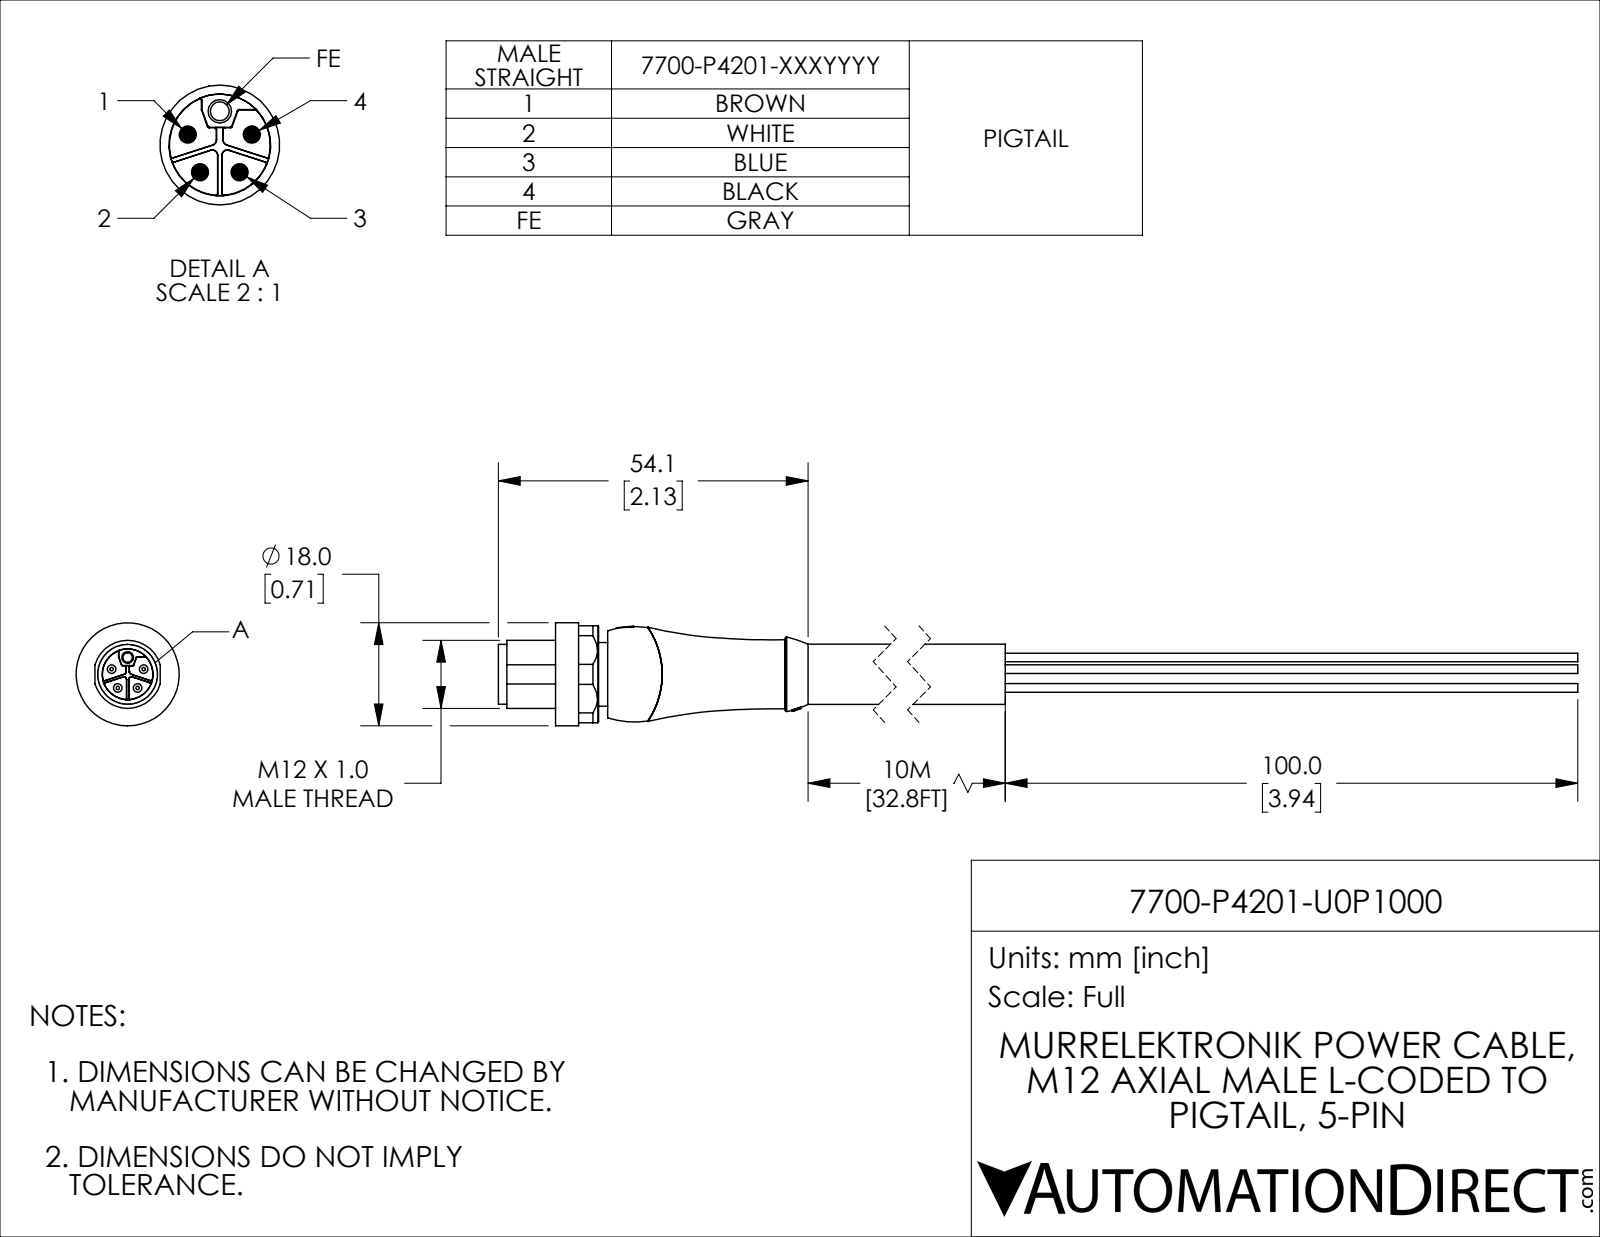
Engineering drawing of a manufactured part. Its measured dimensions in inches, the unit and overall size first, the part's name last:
Units: inches
Overall size (bounding box): 10.004 × 0.709 × 0.709
Round holes (diameter × count): ⌀0.065 ×1
Round bosses / shafts (diameter × count): ⌀0.059 ×5, ⌀0.709 ×1, ⌀0.468 ×1, ⌀0.437 ×1, ⌀0.413 ×1, ⌀0.411 ×1
Partial cylindrical surfaces — rounded edges, fillets, slot ends (radius × count): R0.006 ×6, R0.044 ×1, R0.352 ×1
Main face-to-face distances: 0.358, 0.075, 0.283, 5.673, 5.39, 5.315, 0.667, 0.047, 0.331, 0.406
Volume: 1.067 in³ · Surface area: 14.12 in²
Bodies: 1 solid, 190 faces (87 planar, 51 cylindrical, 52 other)
Part name (STEP PRODUCT): 7700-P4201-U0P1000
STEP written by: SolidWorks 2021 (CONFIG_CONTROL_DESIGN)
